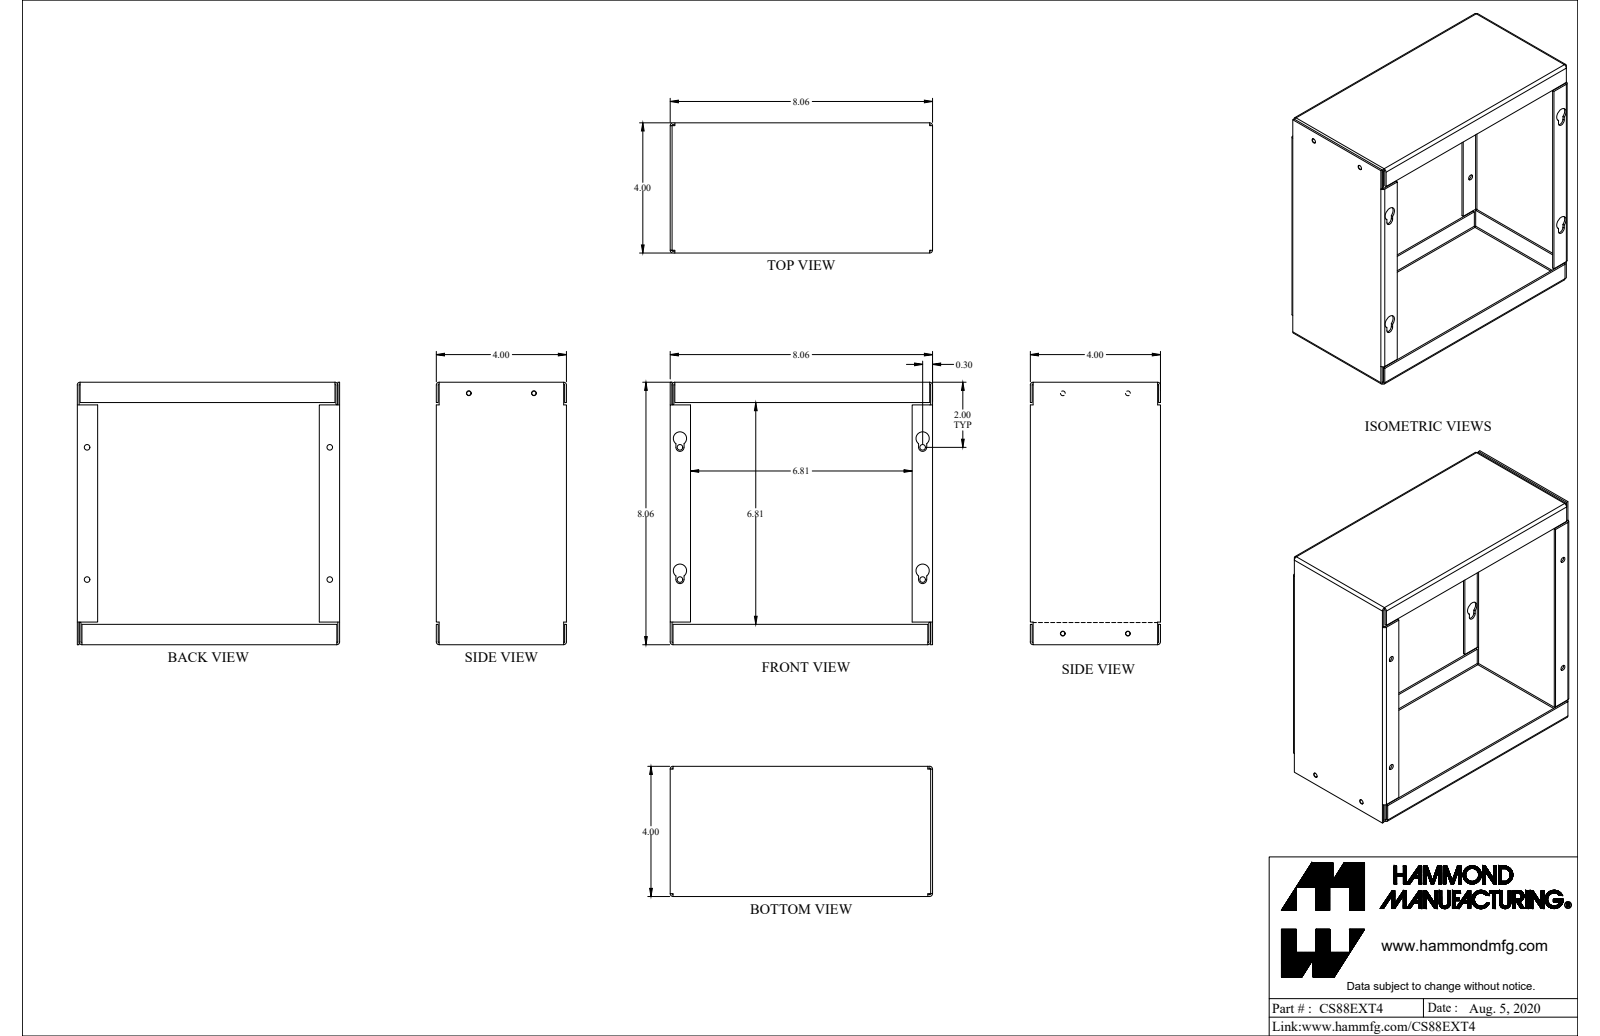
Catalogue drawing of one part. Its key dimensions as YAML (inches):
part_name: "CS88EXT4"
step_written_by: "SolidWorks 2021 (AUTOMOTIVE_DESIGN)"
units: inches
bodies: {solids: 2, faces: 124, planar: 80, cylindrical: 44, other: 0}
overall_size: [8.063, 8.063, 4]
volume: 9.273
surface_area: 331.2
round_holes:
  - {diameter: 0.145, count: 4}
  - {diameter: 0.17, count: 4}
round_bosses_or_shafts:
  - {diameter: 0.131, count: 4}
partial_cylinders:
  - {radius: 0.029, count: 12}
  - {radius: 0.086, count: 12}
  - {radius: 0.125, count: 4}
  - {radius: 0.203, count: 4}
face_to_face_distances: [8.006, 0.057, 0.057, 7.948, 8.063, 8.062, 7.949, 3.943, 3.886, 4]
hole_center_spacings: [2, 4.062, 7.38, 7.459, 7.646, 8.493]
